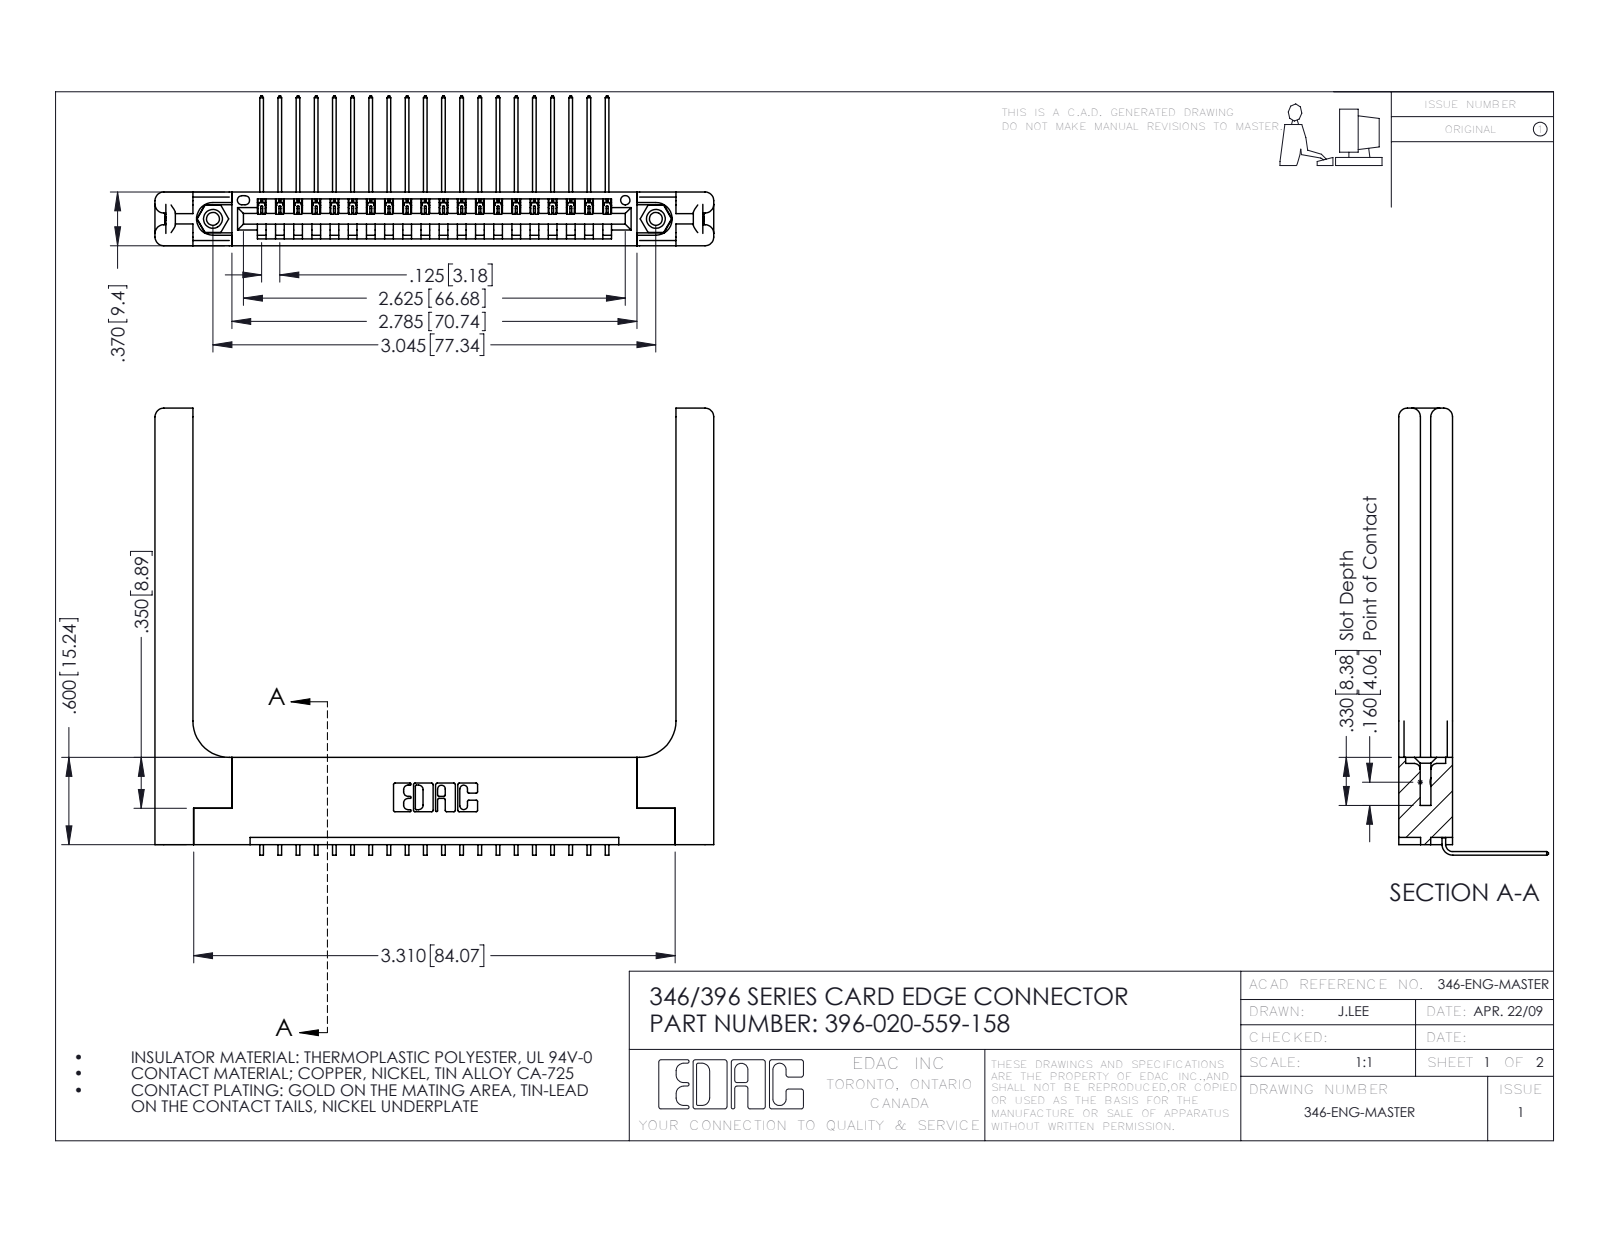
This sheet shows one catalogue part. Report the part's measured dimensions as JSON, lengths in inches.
{"part_name": "346-220-058_345-220-058; 345-250-001_345-250-001-102; 346 Part_Flush Mounting Lugs - 0.156 Dia-TH; 396-020-559-158 (+1 more)", "step_written_by": "SolidWorks 2016 (CONFIG_CONTROL_DESIGN)", "units": "inches", "bodies": {"solids": 25, "faces": 1578, "planar": 1064, "cylindrical": 454, "other": 60}, "overall_size": [3.841, 3.073, 1.03], "volume_in3": 1.024, "surface_area_in2": 26.19, "round_holes": [[0.089, 2], [0.125, 2], [0.156, 2], [0.064, 1]], "round_bosses_or_shafts": [[0.155, 2]], "partial_cylinders_radius": [[0.006, 40], [0.01, 22], [0.06, 16], [0.007, 6], [0.031, 6], [0.026, 3], [0.03, 2], [0.031, 2]], "face_to_face_distances": [0.37, 0.072, 0.048, 0.322, 0.15, 0.148, 0.25, 0.025, 0.298, 0.102], "hole_center_spacings": [0.246, 2.837, 3.045]}
